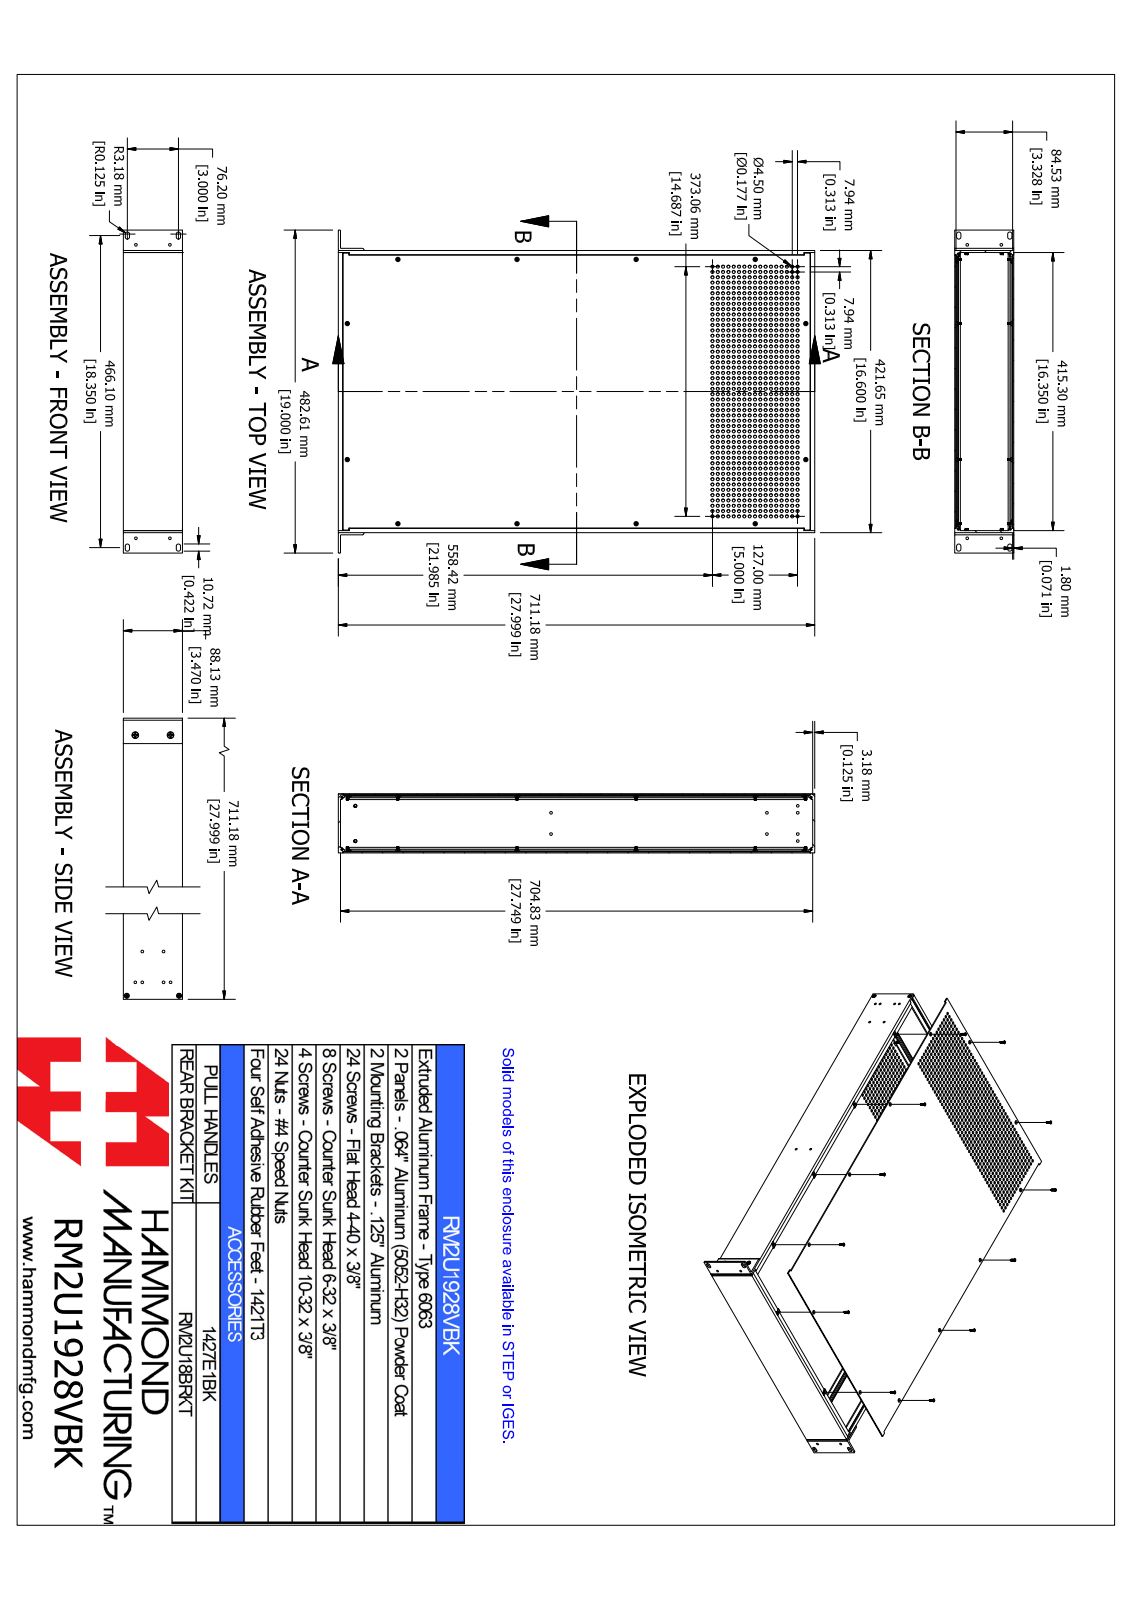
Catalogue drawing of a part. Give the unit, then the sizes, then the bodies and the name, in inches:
Units: inches
Overall size (bounding box): 28.066 × 19 × 3.471
Round holes (diameter × count): ⌀0.177 ×1632, ⌀0.157 ×16, ⌀0.16 ×15, ⌀0.165 ×8, ⌀0.159 ×6, ⌀0.156 ×4, ⌀0.157 ×4, ⌀0.169 ×4, ⌀0.197 ×2
Round bosses / shafts (diameter × count): ⌀0.2 ×15, ⌀0.112 ×15, ⌀0.238 ×8, ⌀0.138 ×8, ⌀0.36 ×2, ⌀0.19 ×2
Partial cylindrical surfaces — rounded edges, fillets, slot ends (radius × count): R0.01 ×96, R0.024 ×96, R0.009 ×48, R0.014 ×48, R0.015 ×16, R0.038 ×16, R0.039 ×16, R0.035 ×11
Main face-to-face distances: 0.071, 3.399, 3.47, 3.328, 0.125, 0.125, 16.6, 16.35, 16.476, 16.475
Hole centre spacings: 7, 14, 17.049, 20.92, 26.707, 8, 12.142, 15.428
Volume: 111.7 in³ · Surface area: 2 671 in²
Bodies: 68 solids, 4268 faces (1076 planar, 2260 cylindrical, 932 other)
Part name (STEP PRODUCT): RM2U1928VBK
STEP written by: SolidWorks 2021 (AUTOMOTIVE_DESIGN)
